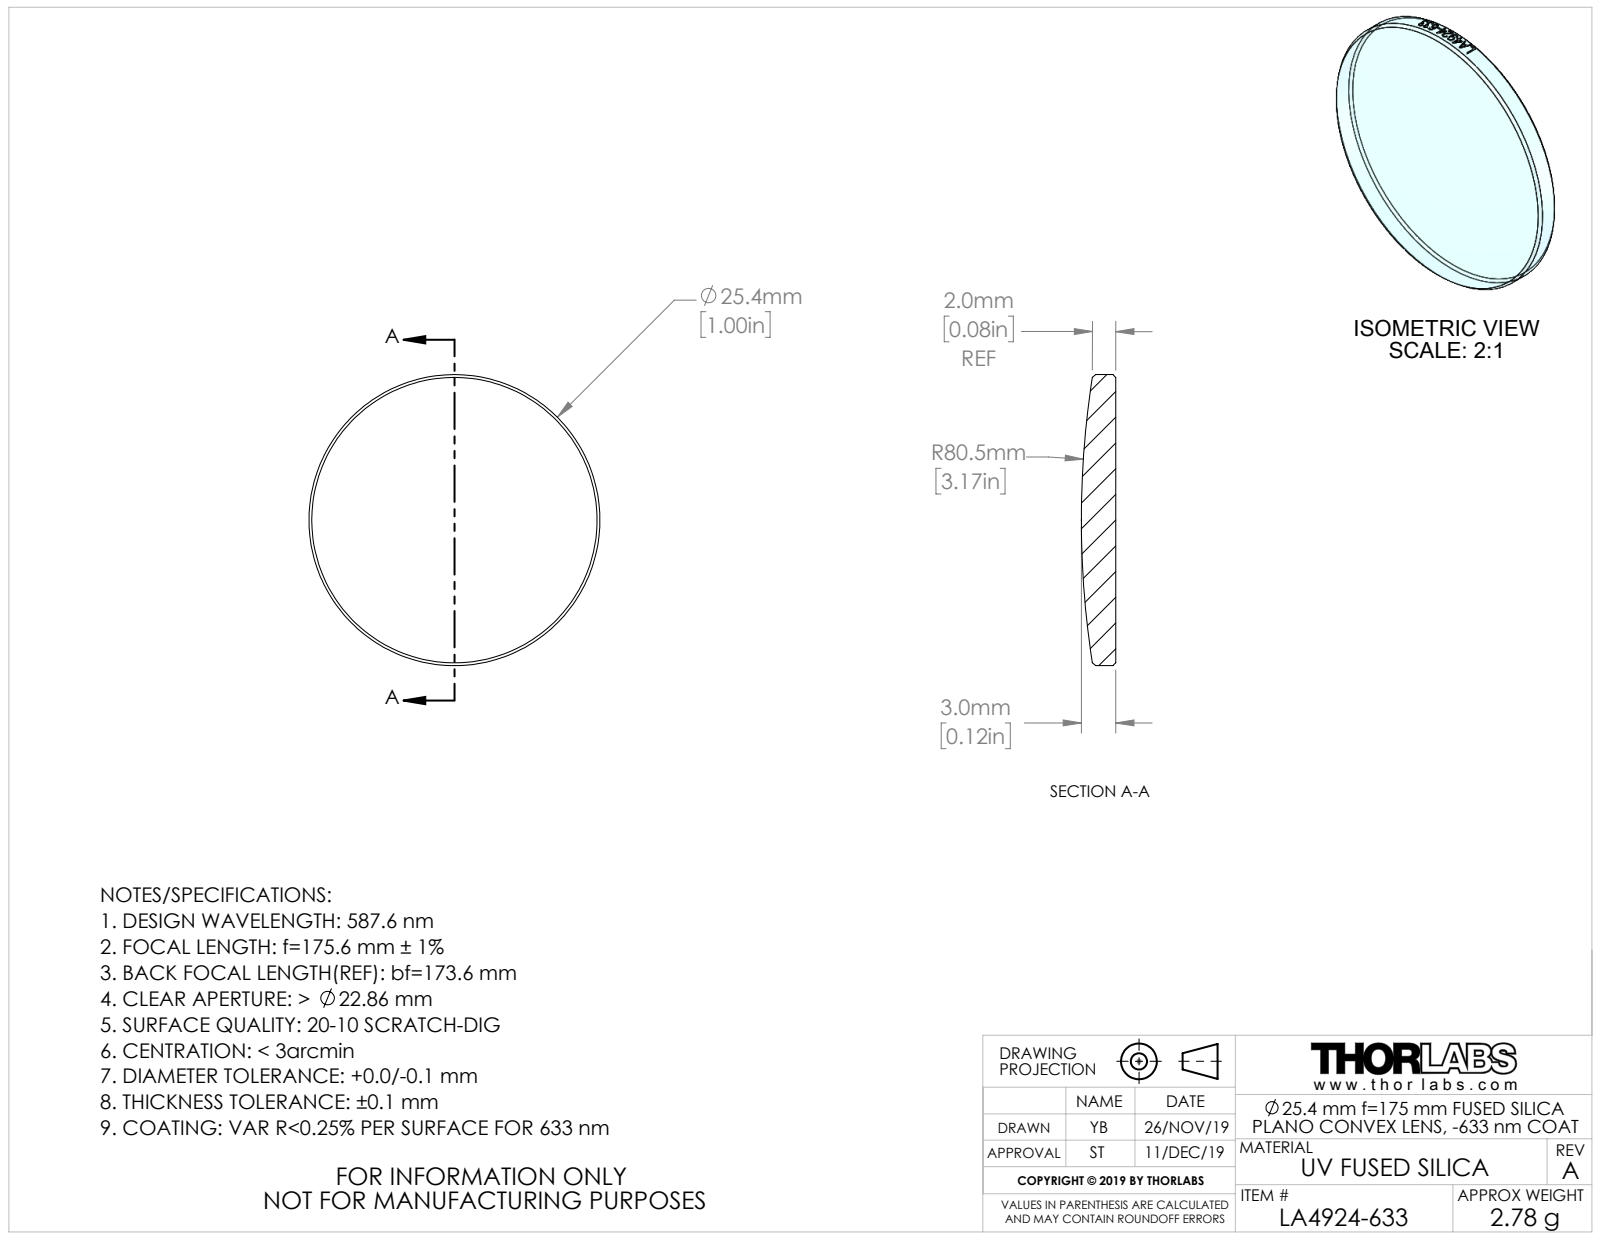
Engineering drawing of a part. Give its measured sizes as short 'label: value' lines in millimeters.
name: CTN015003; CTN014984-999
written by: SolidWorks 2018 (AUTOMOTIVE_DESIGN)
unit: mm
bodies: 1 solid, 29 faces (1 planar, 22 cylindrical, 6 other)
size: 25.4 × 25.4 × 3
volume: 1 263 mm³; area: 1 155 mm²
bosses: 1× ⌀25.4
